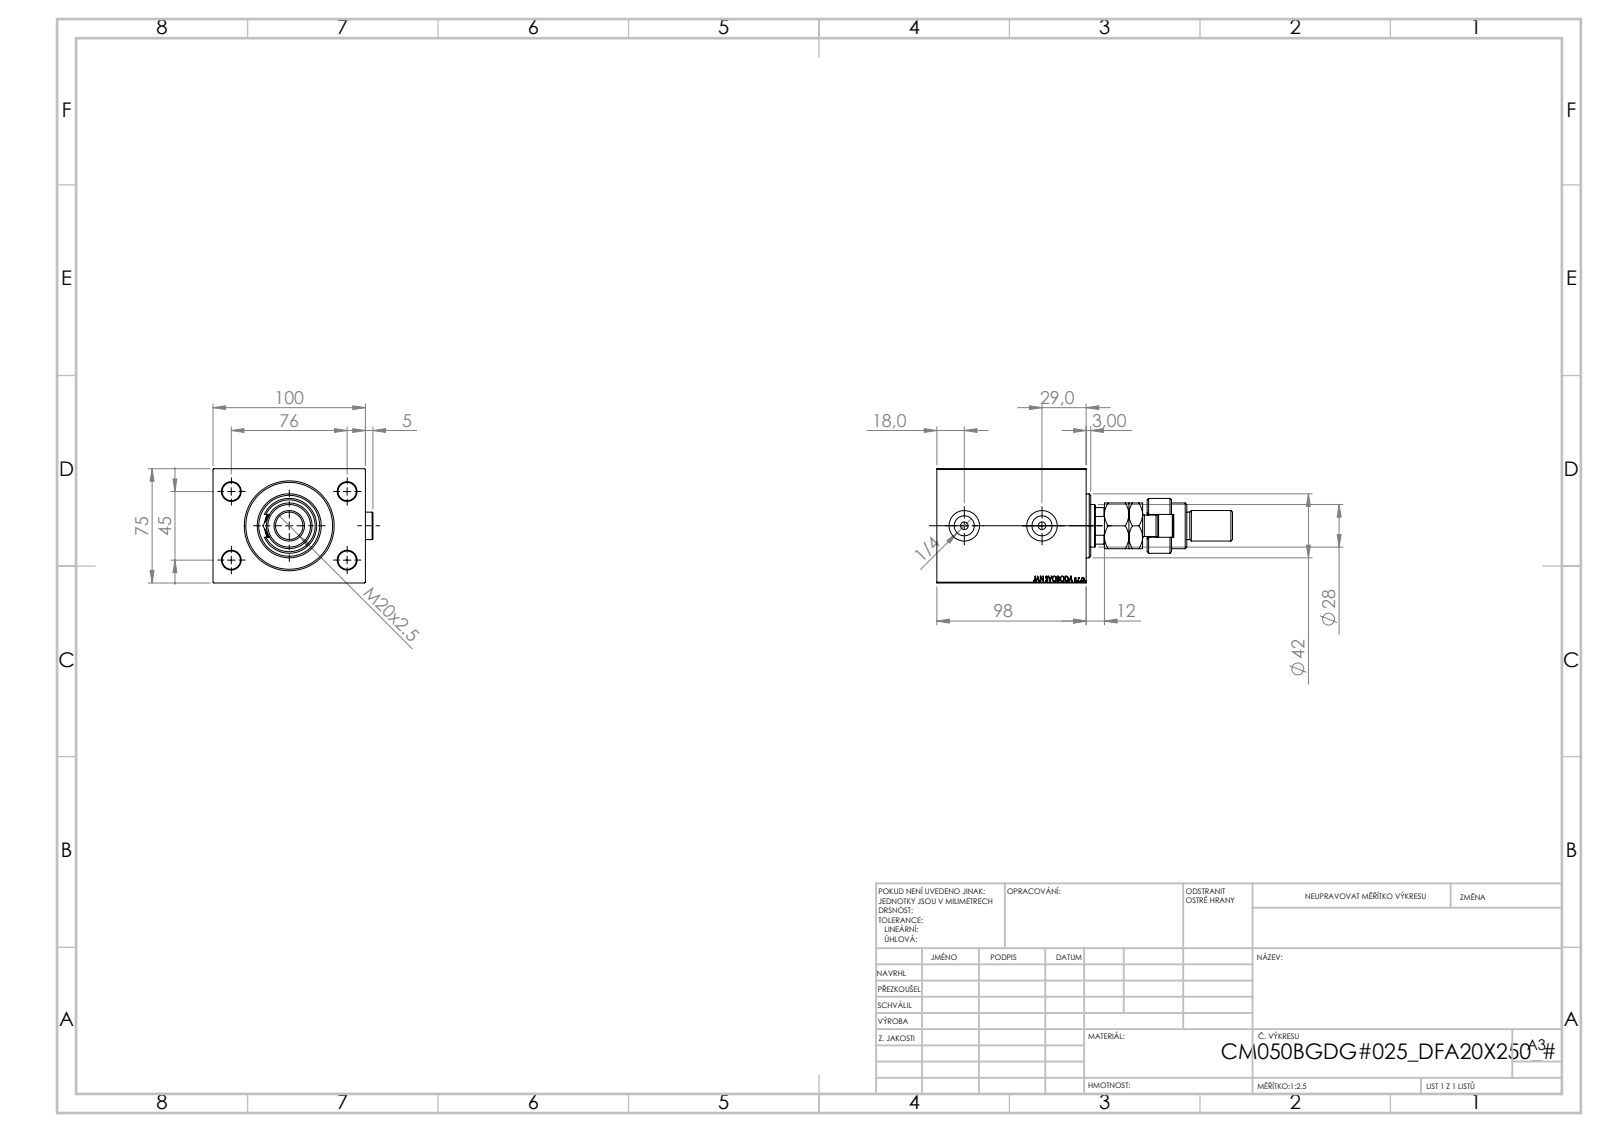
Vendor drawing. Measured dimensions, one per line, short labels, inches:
name: V450CM_B_VCP; Zatka_OIL_PORT; V450CM_VC_B; MFA (+2 more)
written by: SolidWorks 2019 (CONFIG_CONTROL_DESIGN)
unit: in
bodies: 7 solids, 1023 faces (464 planar, 85 cylindrical, 474 other)
size: 7.638 × 4.13 × 2.953
volume: 44.34 in³; area: 172 in²
holes: 4× ⌀0.472, 2× ⌀0.197, 2× ⌀0.518, 2× ⌀0.787, 1× ⌀0.728, 1× ⌀1.102, 1× ⌀1.24, 1× ⌀1.28, 1× ⌀1.969, 1× ⌀2.047, 1× ⌀2.244
bosses: 3× ⌀0.709, 1× ⌀1.654, 1× ⌀1.417, 1× ⌀1.181, 1× ⌀0.866, 1× ⌀0.787, 1× ⌀0.551
rounds: 1× R0.295, 1× R0.472, 1× R0.531
face distances: 2.953, 3.937, 3.858, 3.307, 0.551, 0.472, 1.457, 0.984, 1.929, 1.181
hole spacings: 1.739, 1.772, 2.992, 3.477, 2.008
